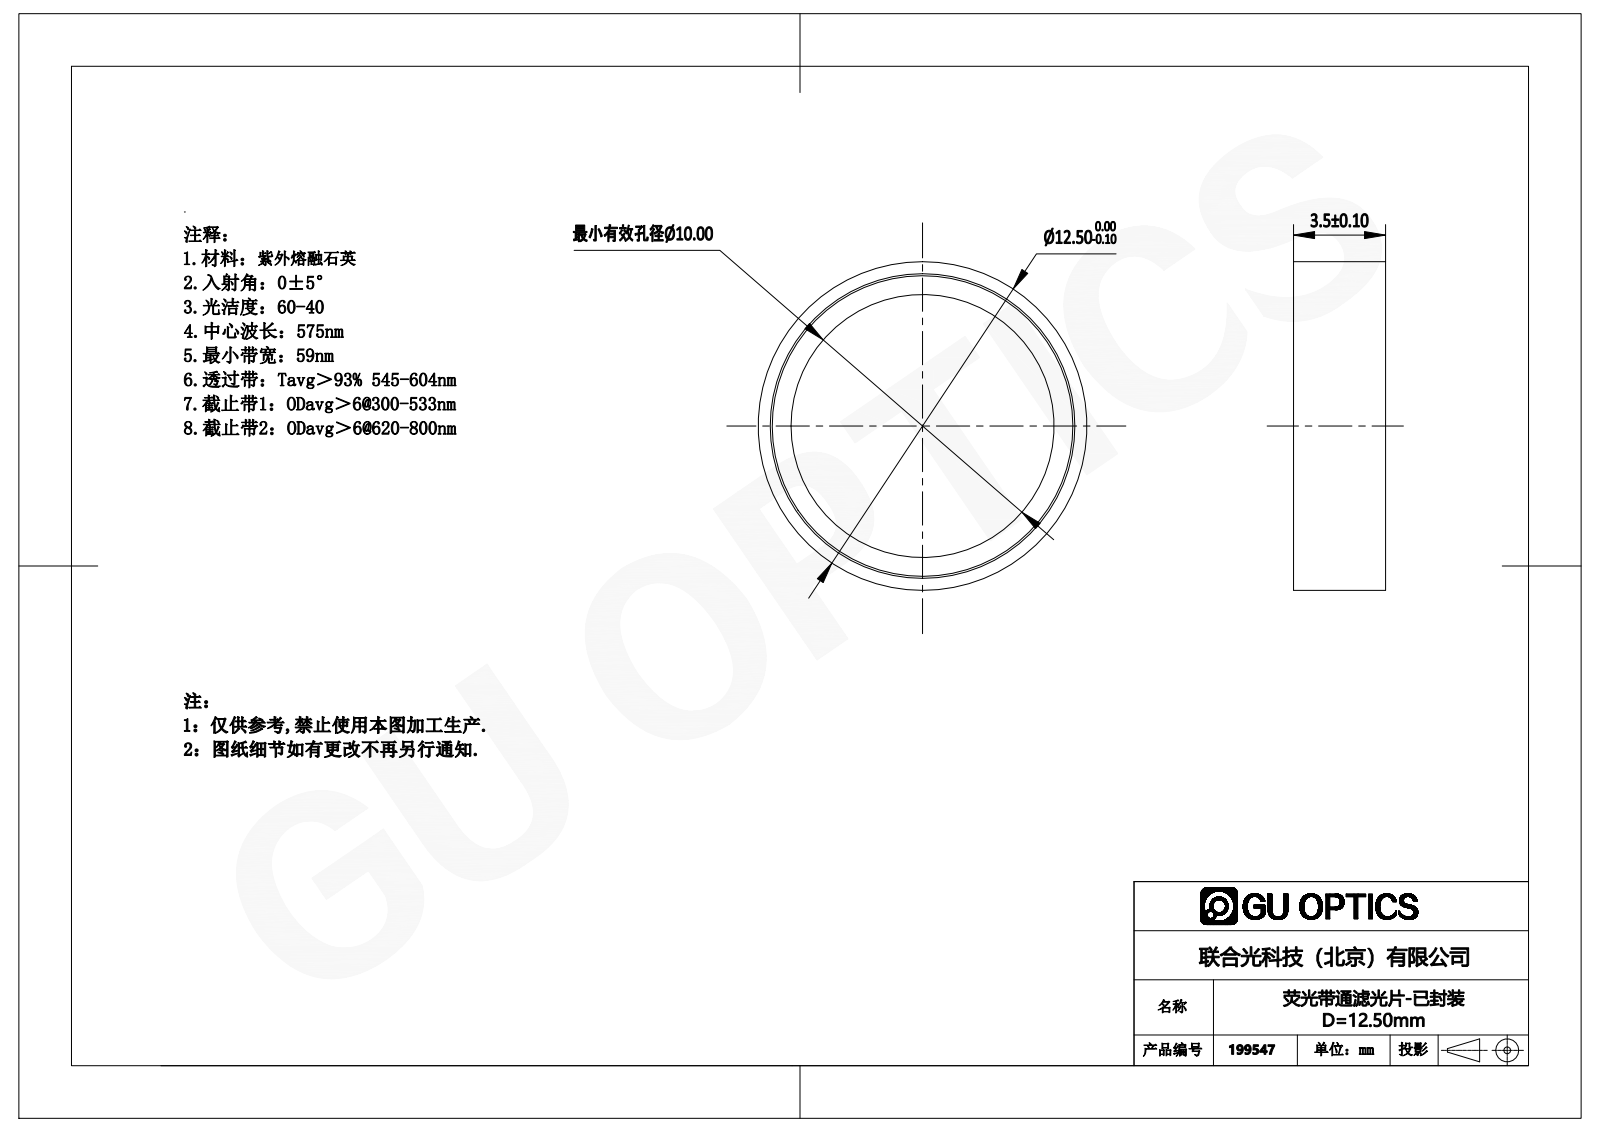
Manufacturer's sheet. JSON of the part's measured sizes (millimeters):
{"part_name": "199409", "step_written_by": "SolidWorks 2019 (CONFIG_CONTROL_DESIGN)", "units": "millimeters", "bodies": {"solids": 3, "faces": 22, "planar": 8, "cylindrical": 14, "other": 0}, "overall_size": [12.5, 12.5, 3.5], "volume_mm3": 297, "surface_area_mm2": 776, "round_holes": [[8.69, 1], [8.81, 1], [11.58, 1], [11.71, 1]], "round_bosses_or_shafts": [[12.5, 1], [11.43, 1], [11.4, 1]], "face_to_face_distances": [2, 0.38, 2.38, 2.76, 3.5, 3.12, 1.12, 0.74, 0.69, 0.31]}
